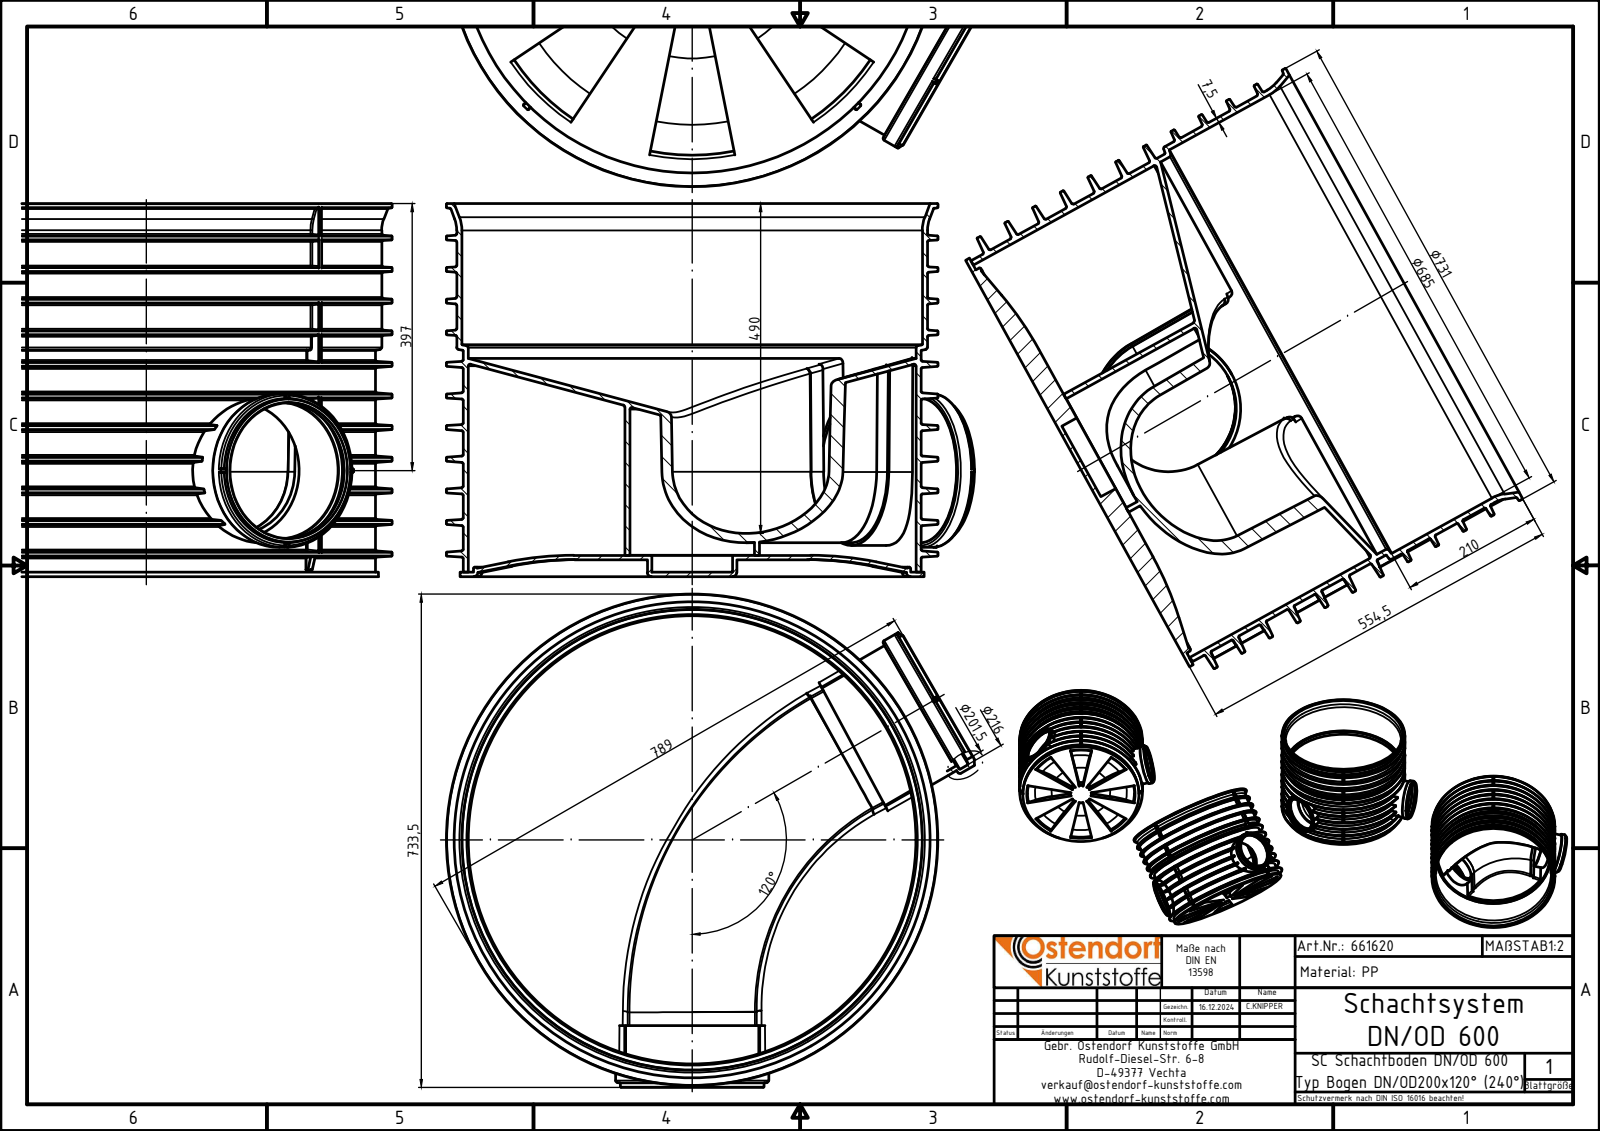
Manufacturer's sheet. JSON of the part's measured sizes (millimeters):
{"part_name": "661620z; 661620 Schacht DN600 Boden; 661620 Schachtboden DN600 Grundkörper", "step_written_by": "Autodesk Inventor 2024 (AUTOMOTIVE_DESIGN)", "units": "millimeters", "bodies": {"solids": 2, "faces": 1543, "planar": 225, "cylindrical": 254, "other": 1064}, "overall_size": [785.43, 733.5, 554.5], "volume_mm3": 25610000, "surface_area_mm2": 5587000, "round_holes": [[201.5, 2], [216, 2], [120, 1], [185, 1], [186.7, 1], [640, 1], [666, 1], [685, 1]], "round_bosses_or_shafts": [[228, 2], [214.5, 2], [213.5, 2], [731, 1], [700, 1], [690, 1], [681, 1], [650, 1]], "partial_cylinders_radius": [[1, 40], [2, 16], [1.5, 4], [93.35, 3], [107.25, 3], [0.8, 2], [111.35, 2], [66.5, 1]], "face_to_face_distances": [6.5, 25, 31.5, 18.5, 554.5, 548, 529.5, 523, 13, 7.5]}
